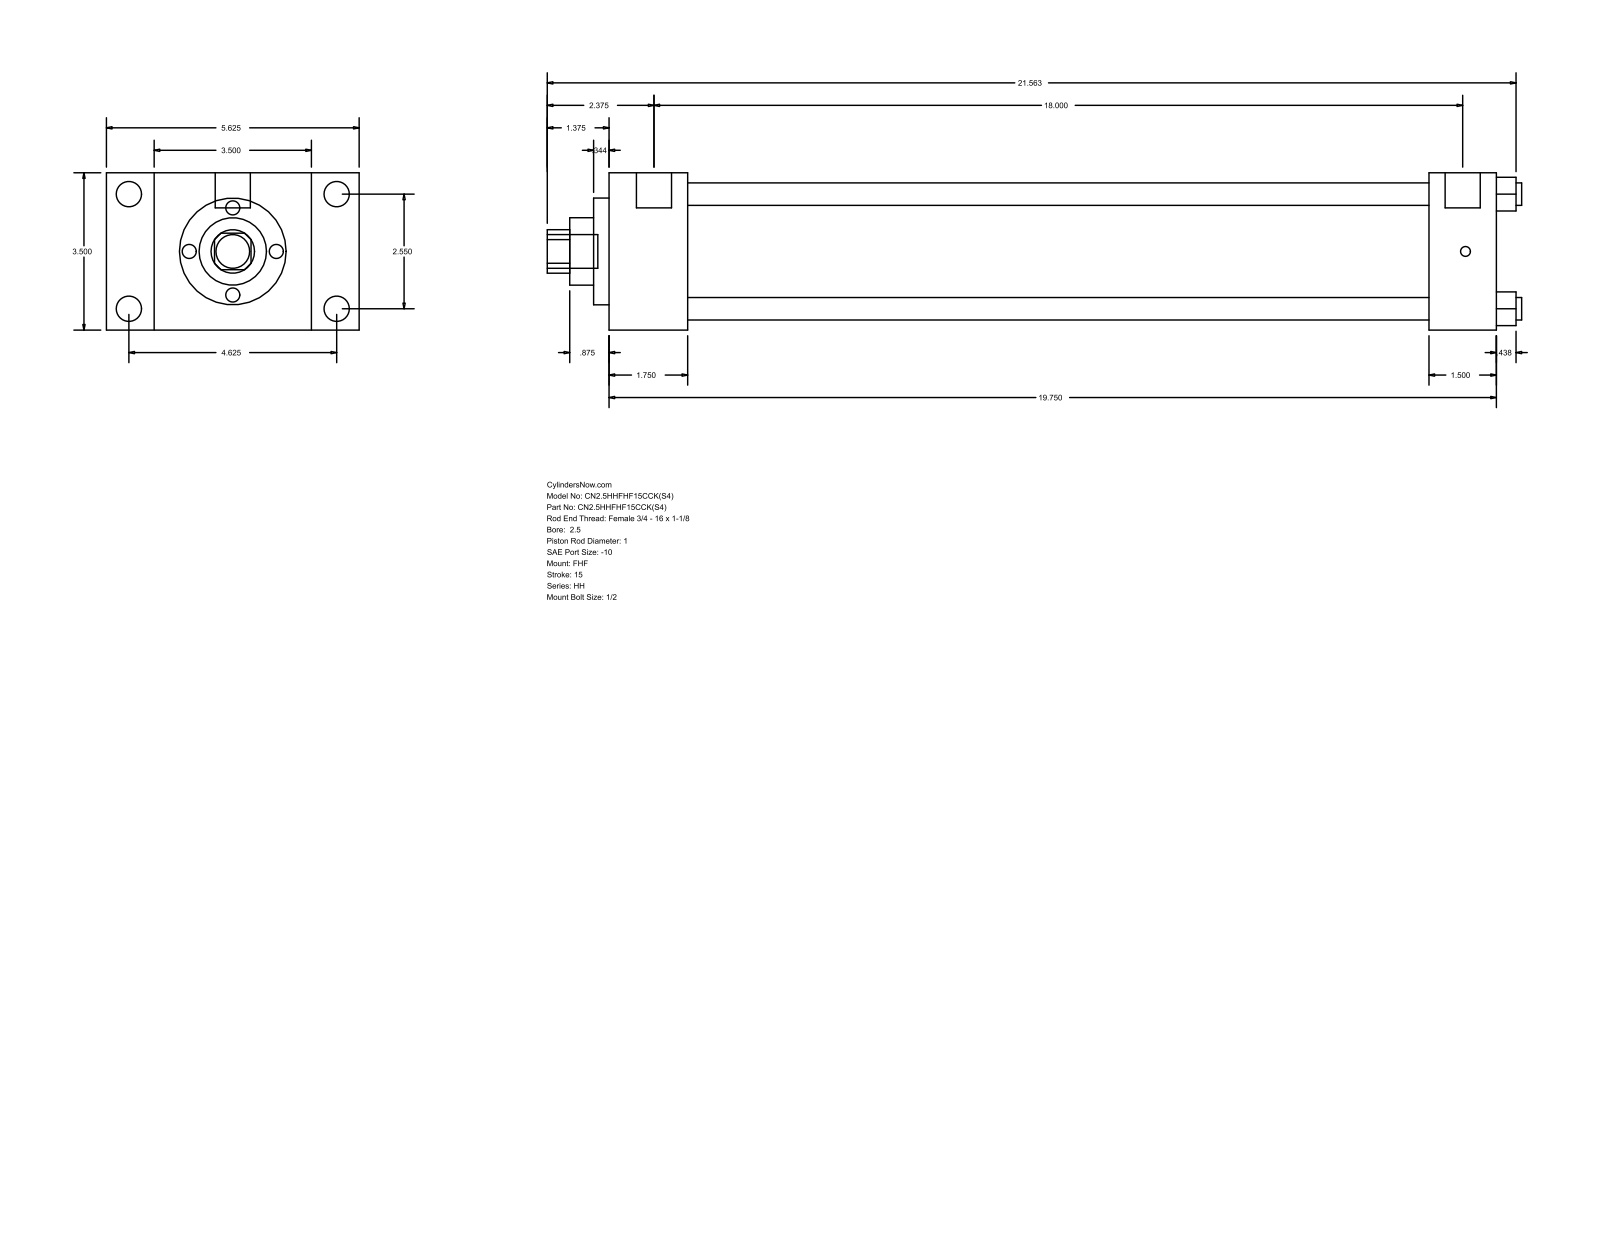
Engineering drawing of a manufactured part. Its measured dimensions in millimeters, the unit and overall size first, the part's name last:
Units: millimetres
Overall size (bounding box): 550.86 × 142.88 × 88.9
Round holes (diameter × count): ⌀12.7 ×4, ⌀25.4 ×1, ⌀38.1 ×1, ⌀60.33 ×1, ⌀73.03 ×1
Round bosses / shafts (diameter × count): ⌀14.3 ×4, ⌀5.56 ×4, ⌀19.84 ×2, ⌀19.05 ×1
Partial cylindrical surfaces — rounded edges, fillets, slot ends (radius × count): R12.29 ×1
Main face-to-face distances: 88.9, 44.46, 26.99, 115.89, 501.66, 457.2, 142.88, 463.56, 419.1, 38.1
Hole centre spacings: 45.79, 64.76, 91.58
Bodies: 0 solids, 90 faces (61 planar, 29 cylindrical, 0 other)
Part name (STEP PRODUCT): HH_FHF__0250_1
STEP written by: GSSL Pune (CONFIG_CONTROL_DESIGN)
